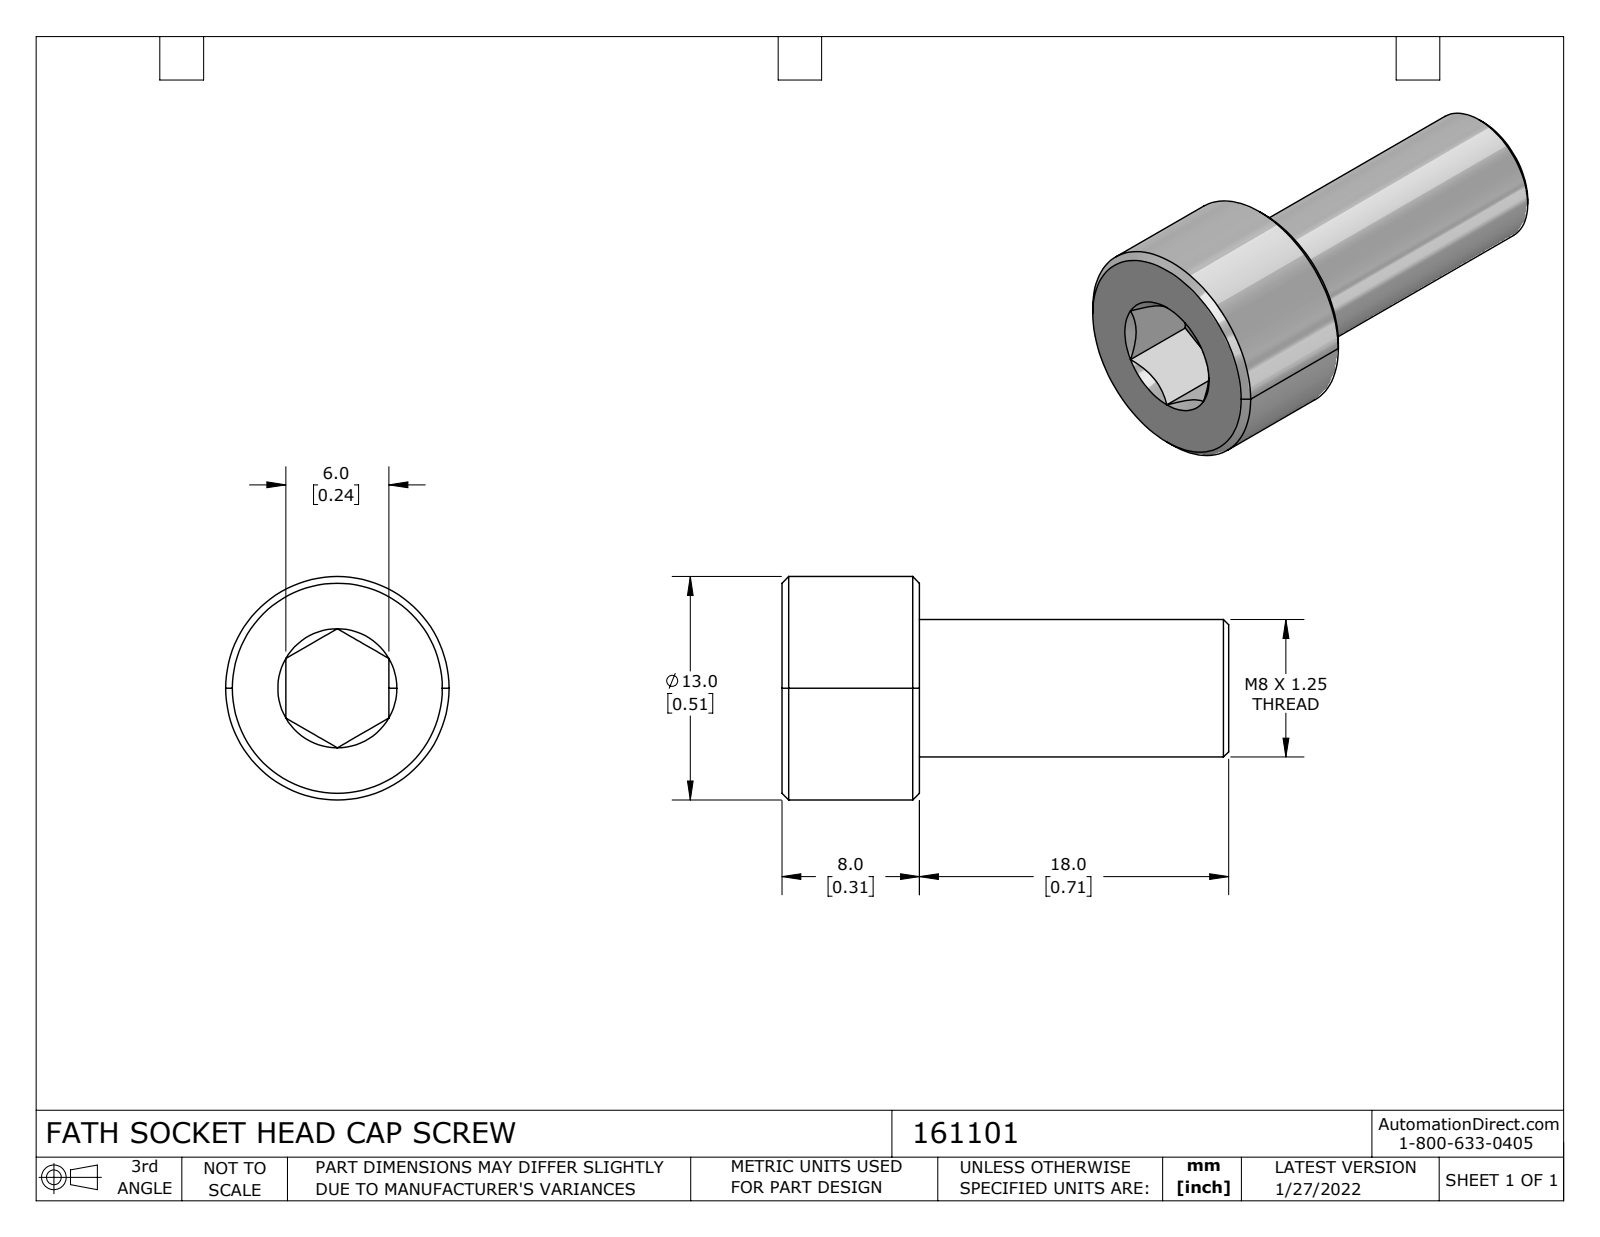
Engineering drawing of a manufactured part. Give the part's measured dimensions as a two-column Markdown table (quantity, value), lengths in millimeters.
| quantity | value |
| --- | --- |
| part name | 161101 |
| STEP written by | SolidWorks 2021 (CONFIG_CONTROL_DESIGN) |
| units | millimeters |
| bodies | 1 solid, 27 faces (10 planar, 4 cylindrical, 13 other) |
| overall size | 26 × 13 × 13 |
| volume | 1 818 mm³ |
| surface area | 1 111 mm² |
| round bosses / shafts (diameter × count) | 13 × 1, 8 × 1 |
| main face-to-face distances | 8, 6, 26, 18, 4.5, 3.5, 21.5 |
